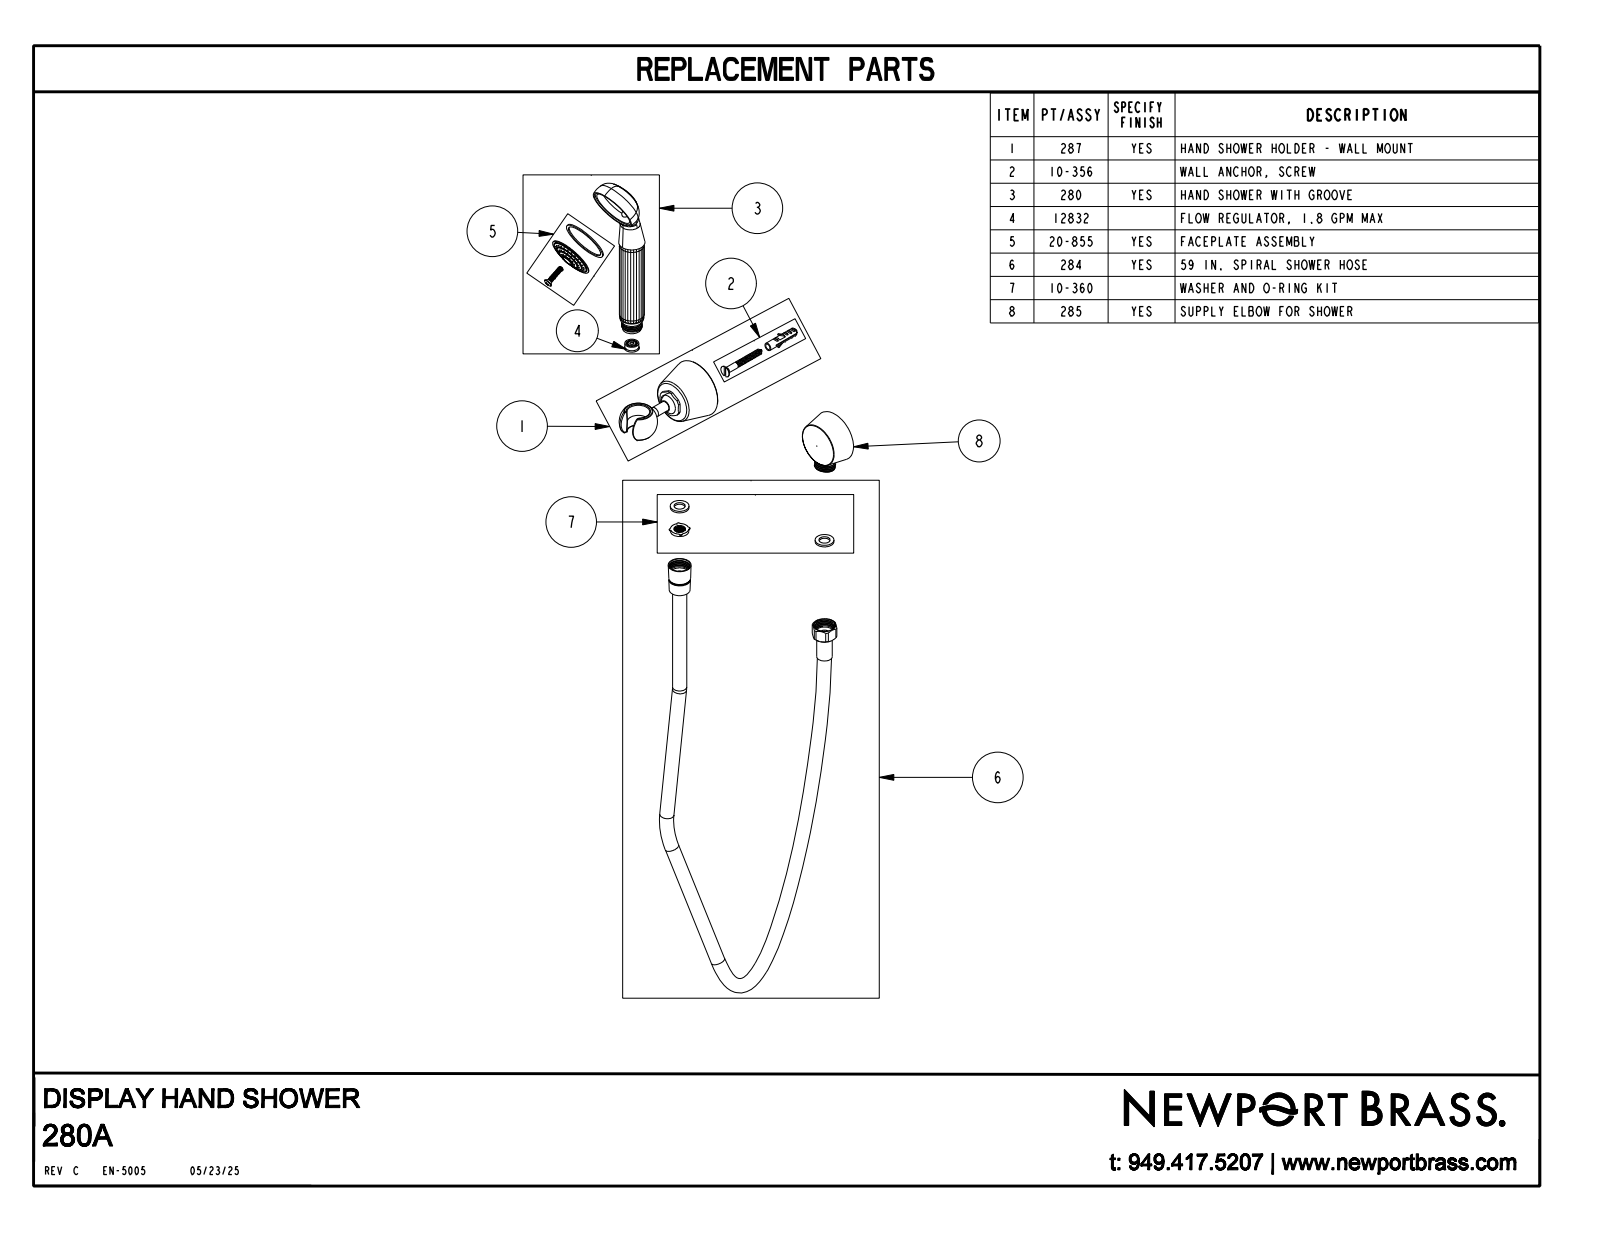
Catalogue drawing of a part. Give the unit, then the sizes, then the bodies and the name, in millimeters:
Units: millimetres
Overall size (bounding box): 699.9 × 330.9 × 192.3
Round holes (diameter × count): ⌀1.2 ×13, ⌀17.1 ×1
Round bosses / shafts (diameter × count): ⌀14.2 ×3, ⌀46.3 ×1, ⌀41.9 ×1, ⌀32 ×1, ⌀23.6 ×1, ⌀23.1 ×1, ⌀21.8 ×1, ⌀21.2 ×1
Partial cylindrical surfaces — rounded edges, fillets, slot ends (radius × count): R0.8 ×4, R10.3 ×1, R12.5 ×1, R13.7 ×1
Main face-to-face distances: 9.7, 30, 22.9, 46.2, 36.6, 16.5, 128.7, 98.7, 25.4, 22.9
Hole centre spacings: 4.7, 12.6, 9, 4.7, 9, 15.3, 16.7, 16.9
Volume: 462 900 mm³ · Surface area: 100 700 mm²
Bodies: 1 solid, 362 faces (53 planar, 77 cylindrical, 232 other)
Part name (STEP PRODUCT): 280A
STEP written by: CREO PARAMETRIC BY PTC INC, 2018400 (CONFIG_CONTROL_DESIGN)
